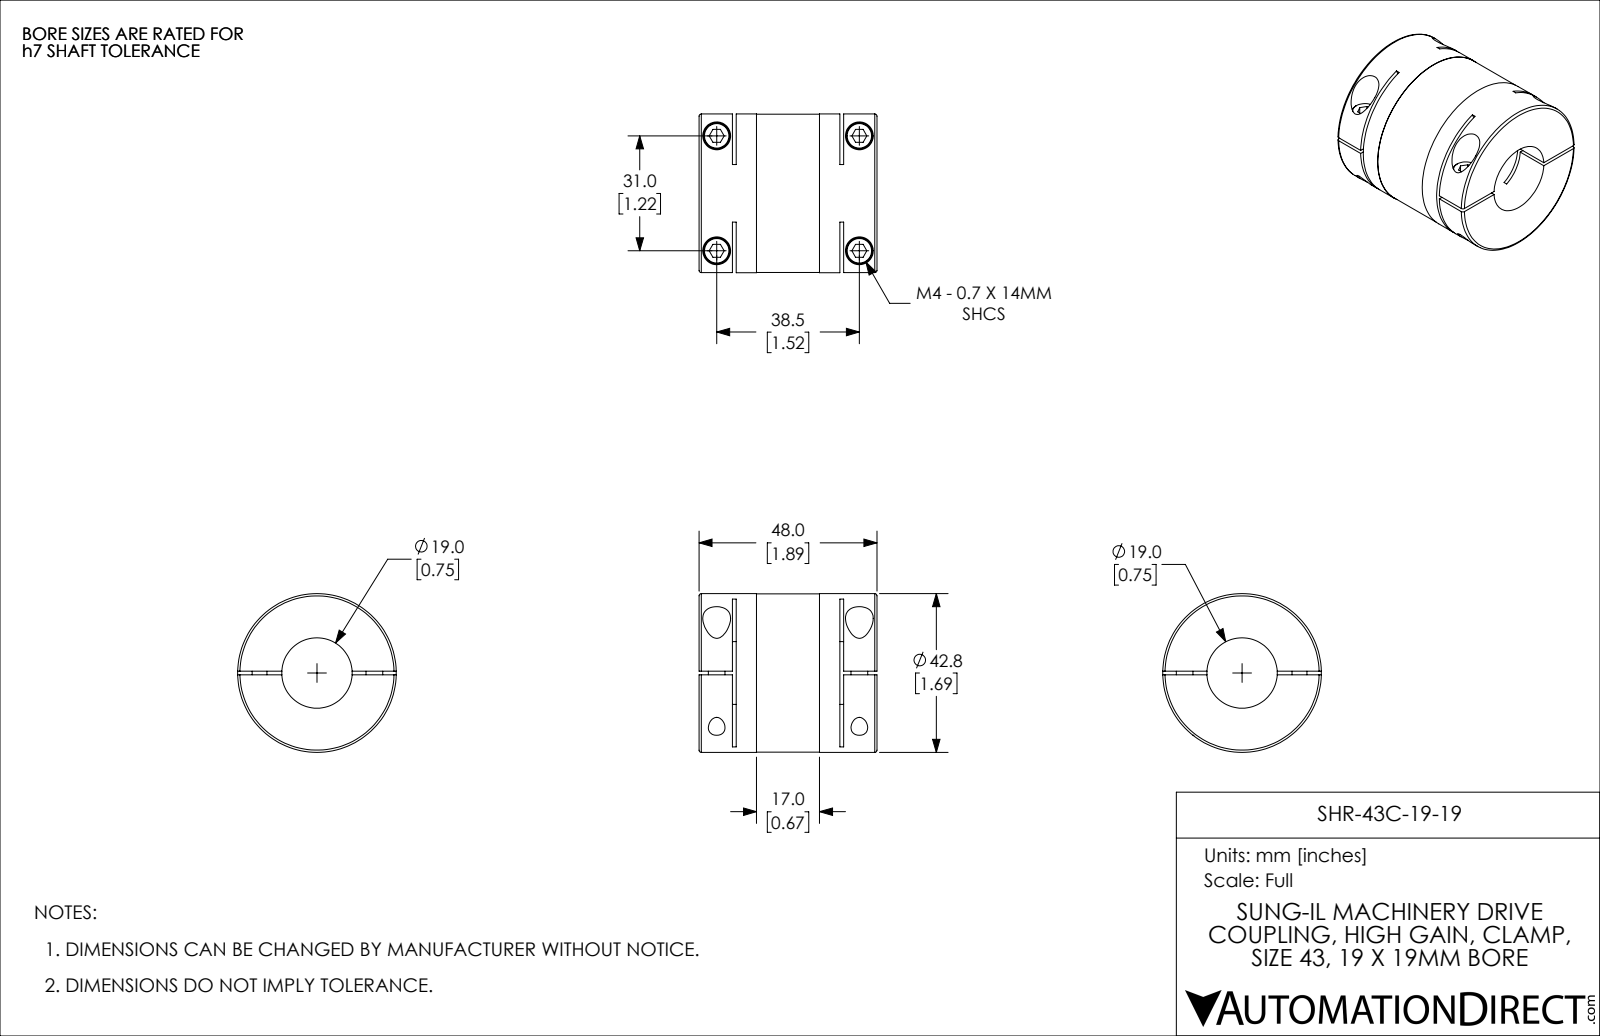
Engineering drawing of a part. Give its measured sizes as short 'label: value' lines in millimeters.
name: SHR-43C-19-19
written by: SolidWorks 2021 (CONFIG_CONTROL_DESIGN)
unit: mm
bodies: 1 solid, 144 faces (70 planar, 58 cylindrical, 16 other)
size: 48 × 42.8 × 42.8
volume: 50 623 mm³; area: 17 932 mm²
holes: 4× ⌀4.5, 4× ⌀7.5, 1× ⌀19, 1× ⌀21
bosses: 4× ⌀7, 2× ⌀4, 1× ⌀42.8, 1× ⌀42.7
rounds: 2× R50
face distances: 1, 10, 38, 9, 39, 29, 48, 28, 30, 15.5
hole spacings: 31, 38.5, 49.43
